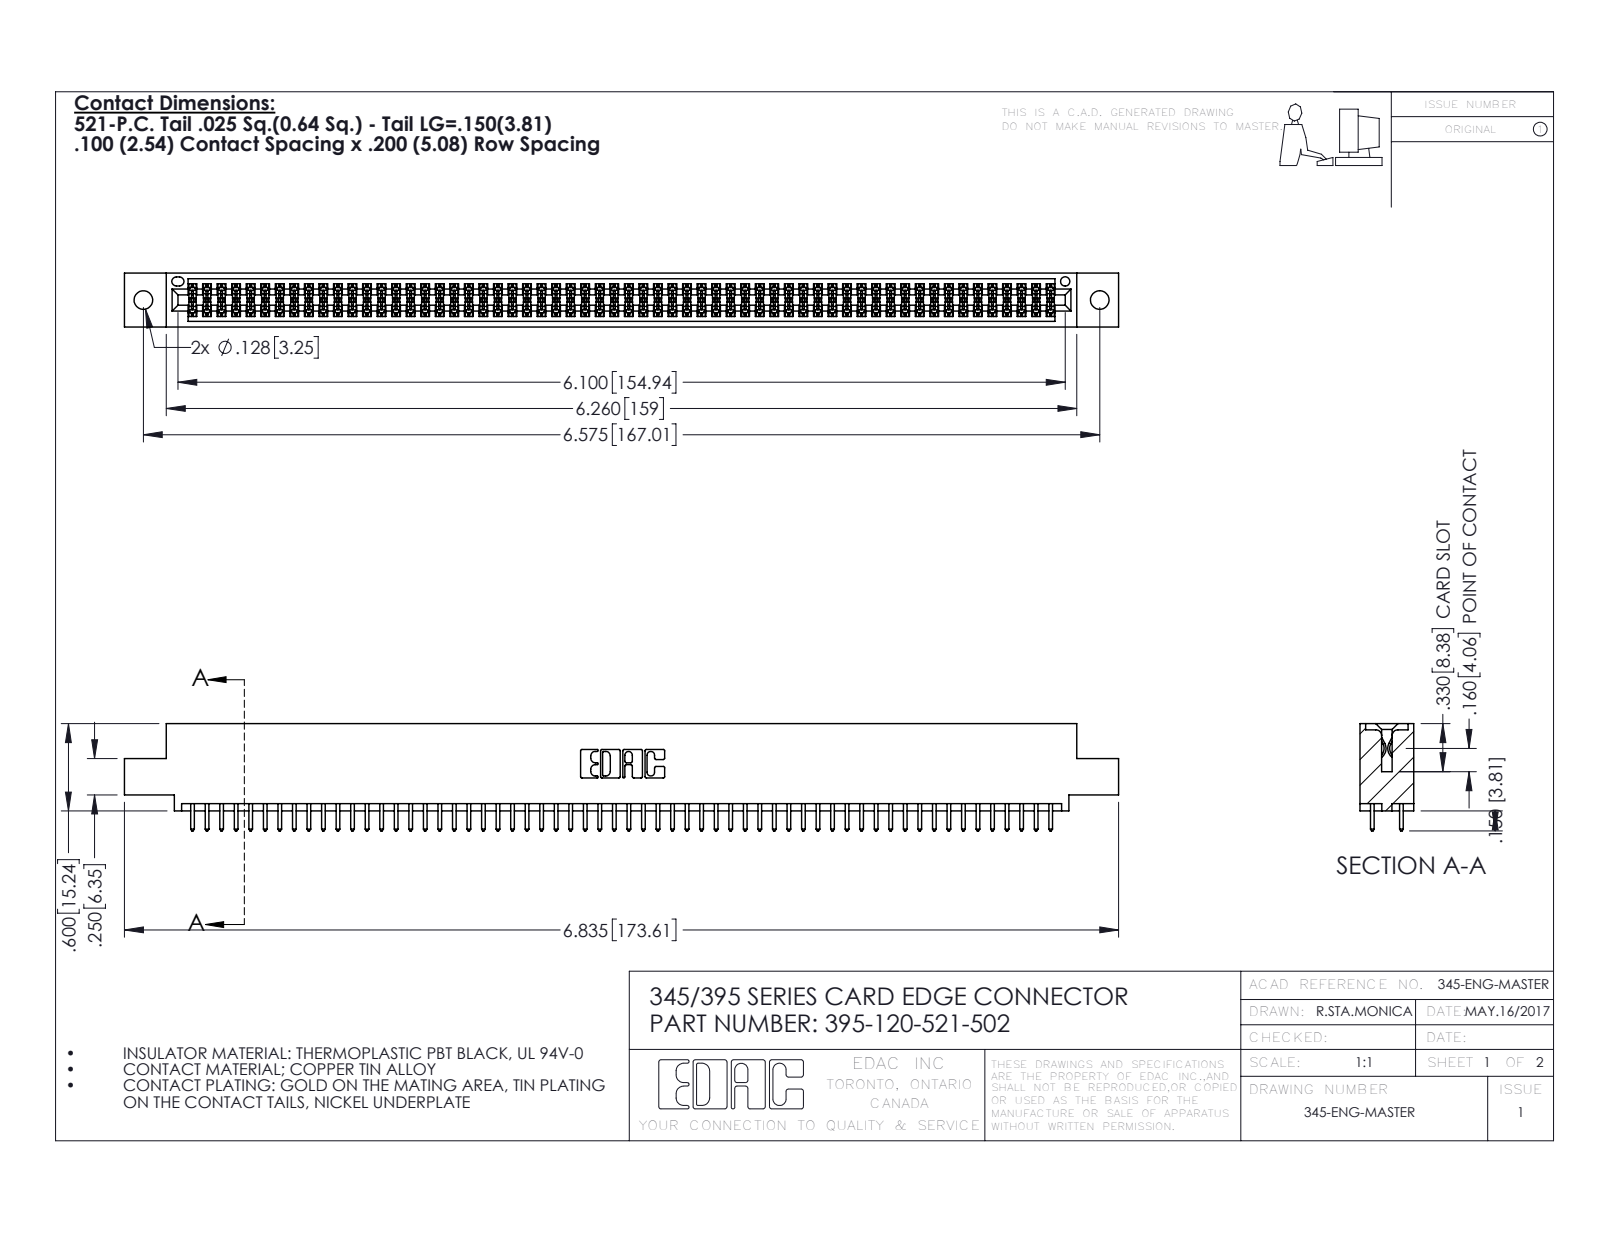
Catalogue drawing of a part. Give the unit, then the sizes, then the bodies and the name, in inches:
Units: inches
Overall size (bounding box): 6.835 × 0.737 × 0.37
Round holes (diameter × count): ⌀0.128 ×2, ⌀0.064 ×1
Partial cylindrical surfaces — rounded edges, fillets, slot ends (radius × count): R0.006 ×180, R0.01 ×120, R0.01 ×22, R0.007 ×6, R0.031 ×6, R0.026 ×3, R0.014 ×2, R0.019 ×2
Main face-to-face distances: 0.072, 0.298, 0.2, 0.098, 0.272, 0.025, 0.37, 0.225, 0.175, 0.149
Hole centre spacings: 0.27, 6.339, 6.575
Volume: 1.03 in³ · Surface area: 38.43 in²
Bodies: 121 solids, 6130 faces (4044 planar, 2086 cylindrical, 0 other)
Part name (STEP PRODUCT): 345-292-001_345-293-121; 395-120-521-502; 345 Part_0.110 Offset - 0.128 Dia
STEP written by: SolidWorks 2016 (CONFIG_CONTROL_DESIGN)
